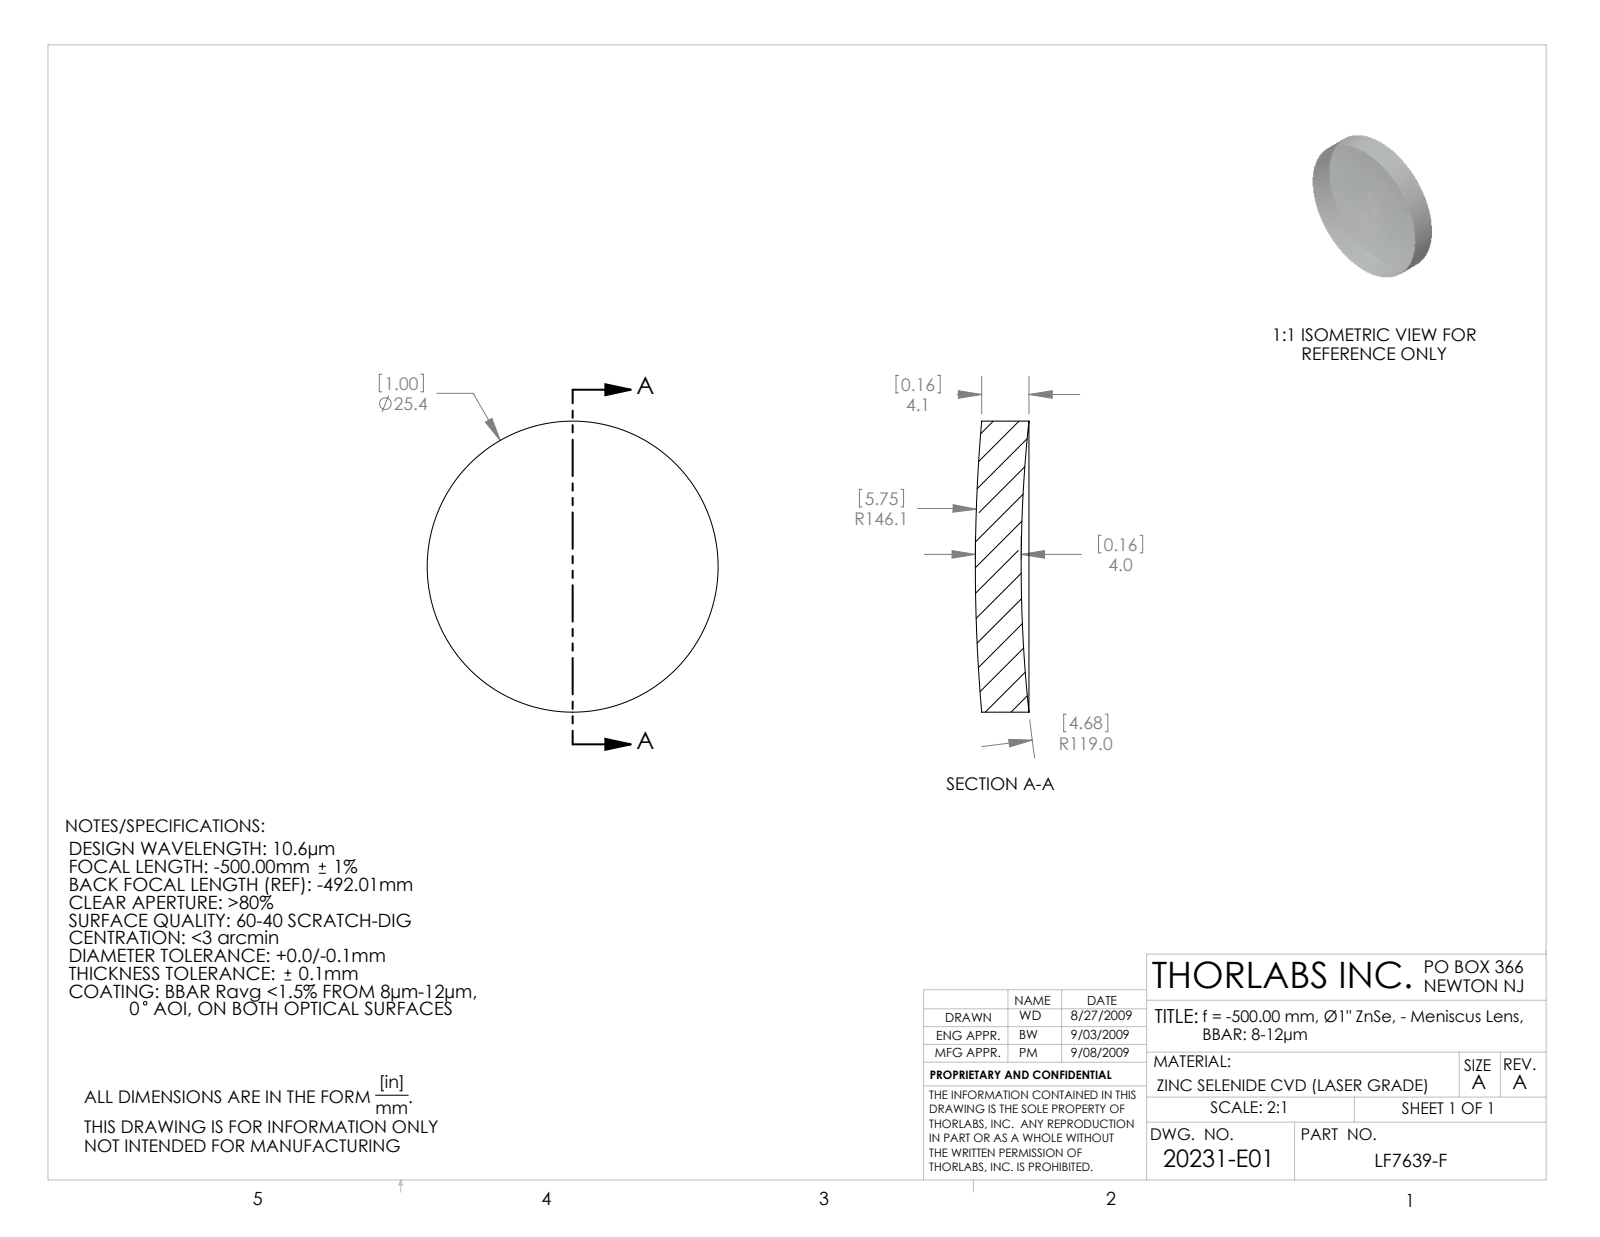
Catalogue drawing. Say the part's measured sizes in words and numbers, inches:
The part is named "20231-E0W". Its 3-D file was written by "SolidWorks 2007 (CONFIG_CONTROL_DESIGN)". It is 1 solid with 6 faces: 0 planar, 2 cylindrical and 4 other. Overall it measures 1 by 1 by 0.184 inches. Its volume is 0.126 cubic inches and its surface area 2.085 square inches. Round bosses or shafts: 1 of diameter 1.
